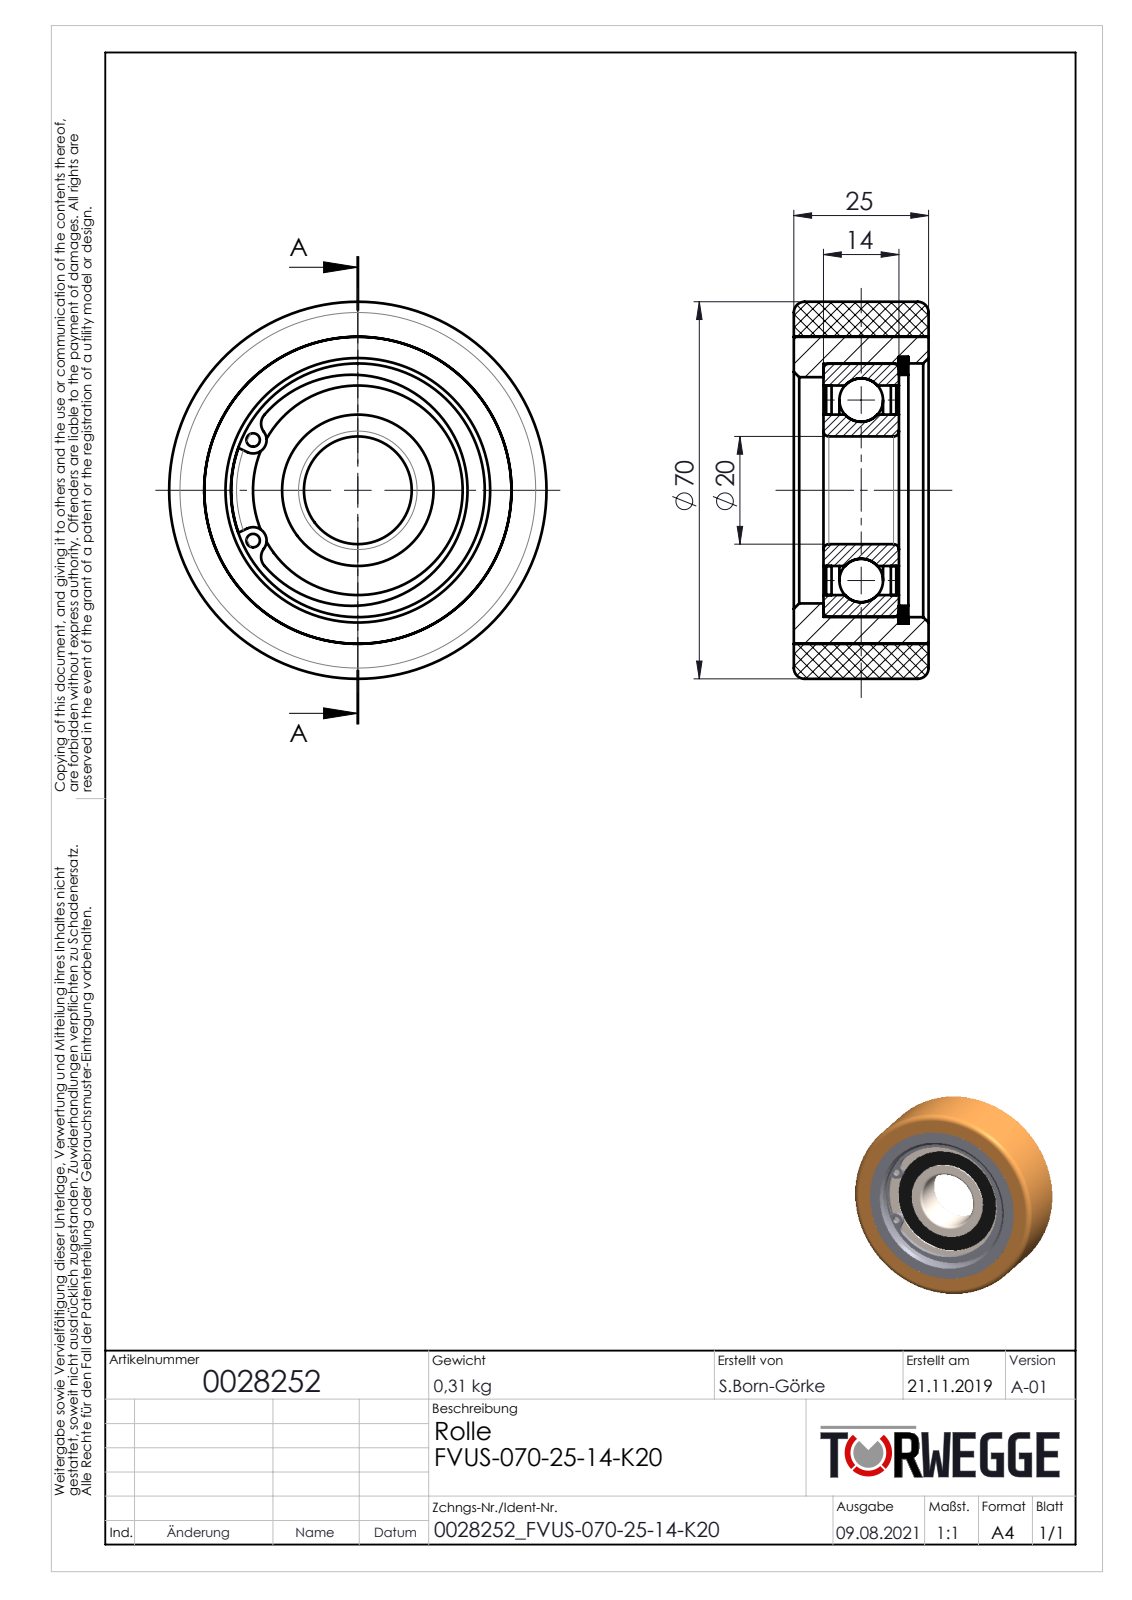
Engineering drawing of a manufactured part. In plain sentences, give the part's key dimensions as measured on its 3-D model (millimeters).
The part is named "0028252". Its 3-D file was written by "SolidWorks 2020 (AUTOMOTIVE_DESIGN)". It is 8 solids with 90 faces: 19 planar, 45 cylindrical and 26 other. Overall it measures 70 by 70 by 25 millimeters. Its volume is 71 930 cubic millimeters and its surface area 37 194 square millimeters. Round holes: 2 of diameter 2.5, 1 of diameter 20, 1 of diameter 28.1, 1 of diameter 38.9, 1 of diameter 42, 1 of diameter 47, 1 of diameter 47.1, 1 of diameter 49.5, 1 of diameter 57. Round bosses or shafts: 1 of diameter 70. Partial cylindrical surfaces (rounded edges, fillets, slot ends): 4 of radius 2.5, 1 of radius 21.45. The main face-to-face distances are 5.5, 19.5, 25, 6, 7, 18, 19, 0.5, 1.5, 12.5. The hole center spacings are 21.55, 18.68.
